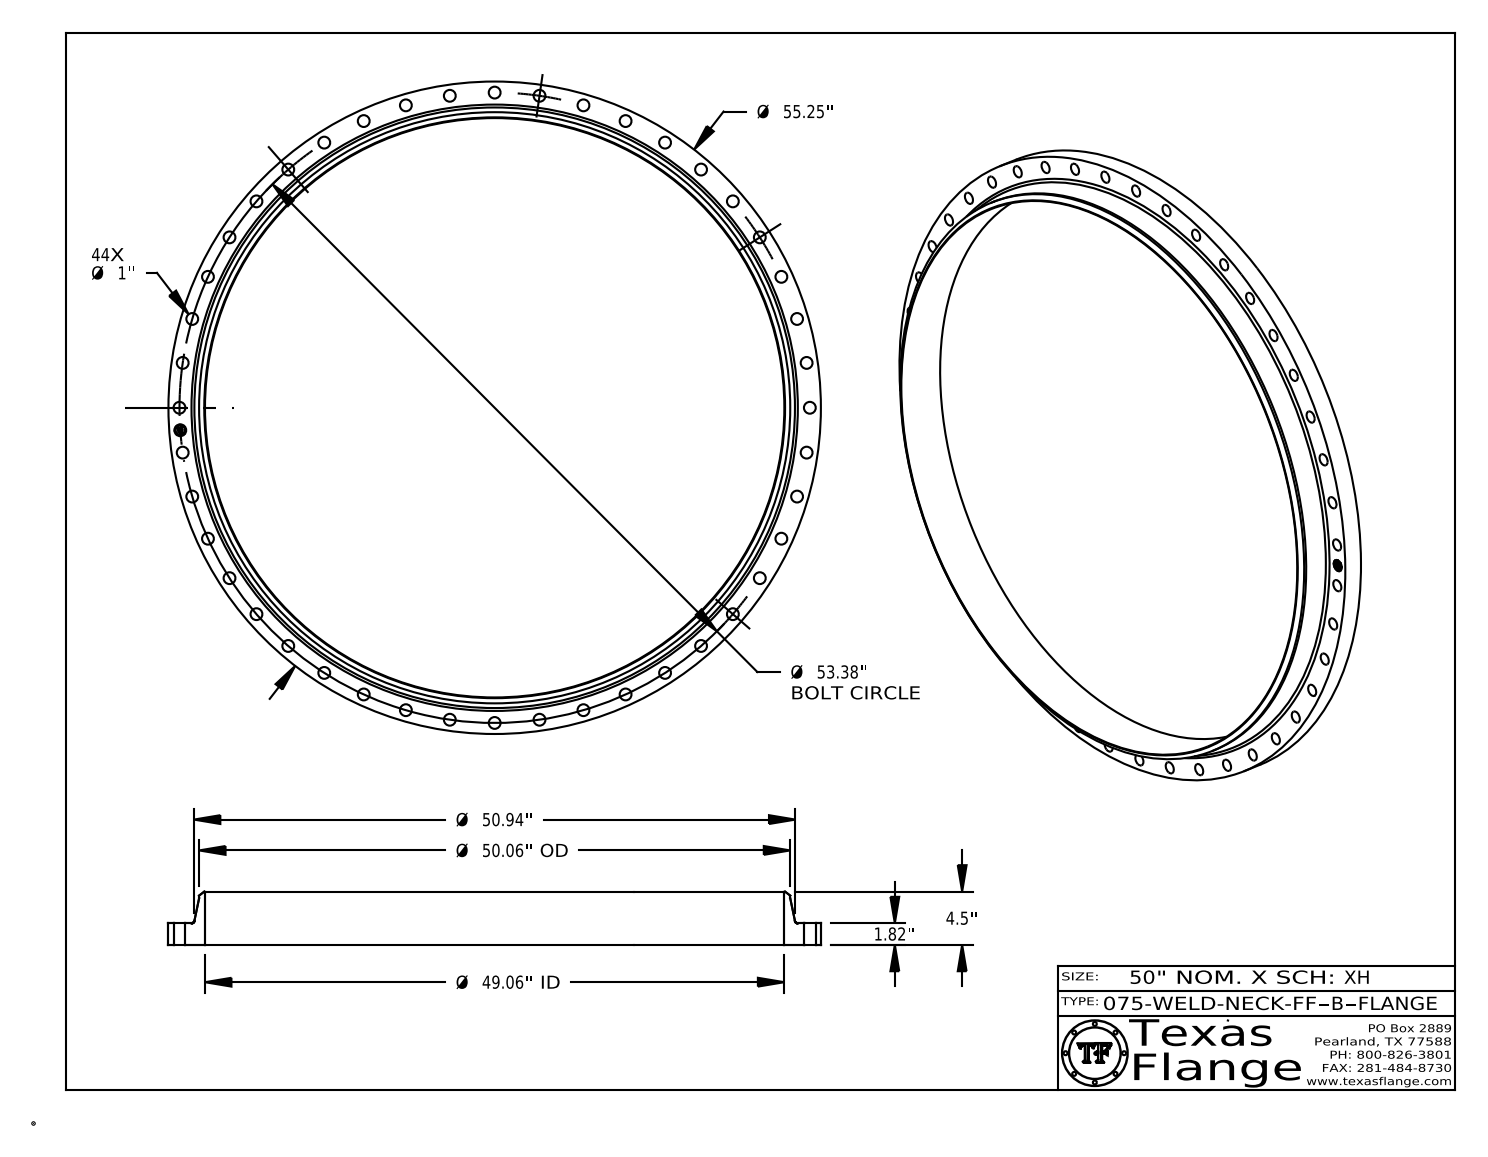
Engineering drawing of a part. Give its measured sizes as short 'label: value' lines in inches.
name: 075-WELD-NECK-FF, Series B
written by: CATIA V5 STEP AP214 (AUTOMOTIVE_DESIGN)
unit: in
bodies: 1 solid, 488 faces (368 planar, 114 cylindrical, 6 other)
size: 55.25 × 55.25 × 4.5
volume: 1 132 in³; area: 2 523 in²
holes: 45× ⌀1, 1× ⌀49.06
bosses: 8× ⌀0.061, 1× ⌀55.25, 1× ⌀50.06, 1× ⌀0.788
face distances: 1.82, 4.5, 2.68, 1.805, 0.015, 2.695, 0.298, 0.292, 0.054, 0.193
hole spacings: 26.69, 7.597, 52.837, 15.039, 51.218, 3.808, 50.015, 52.16
